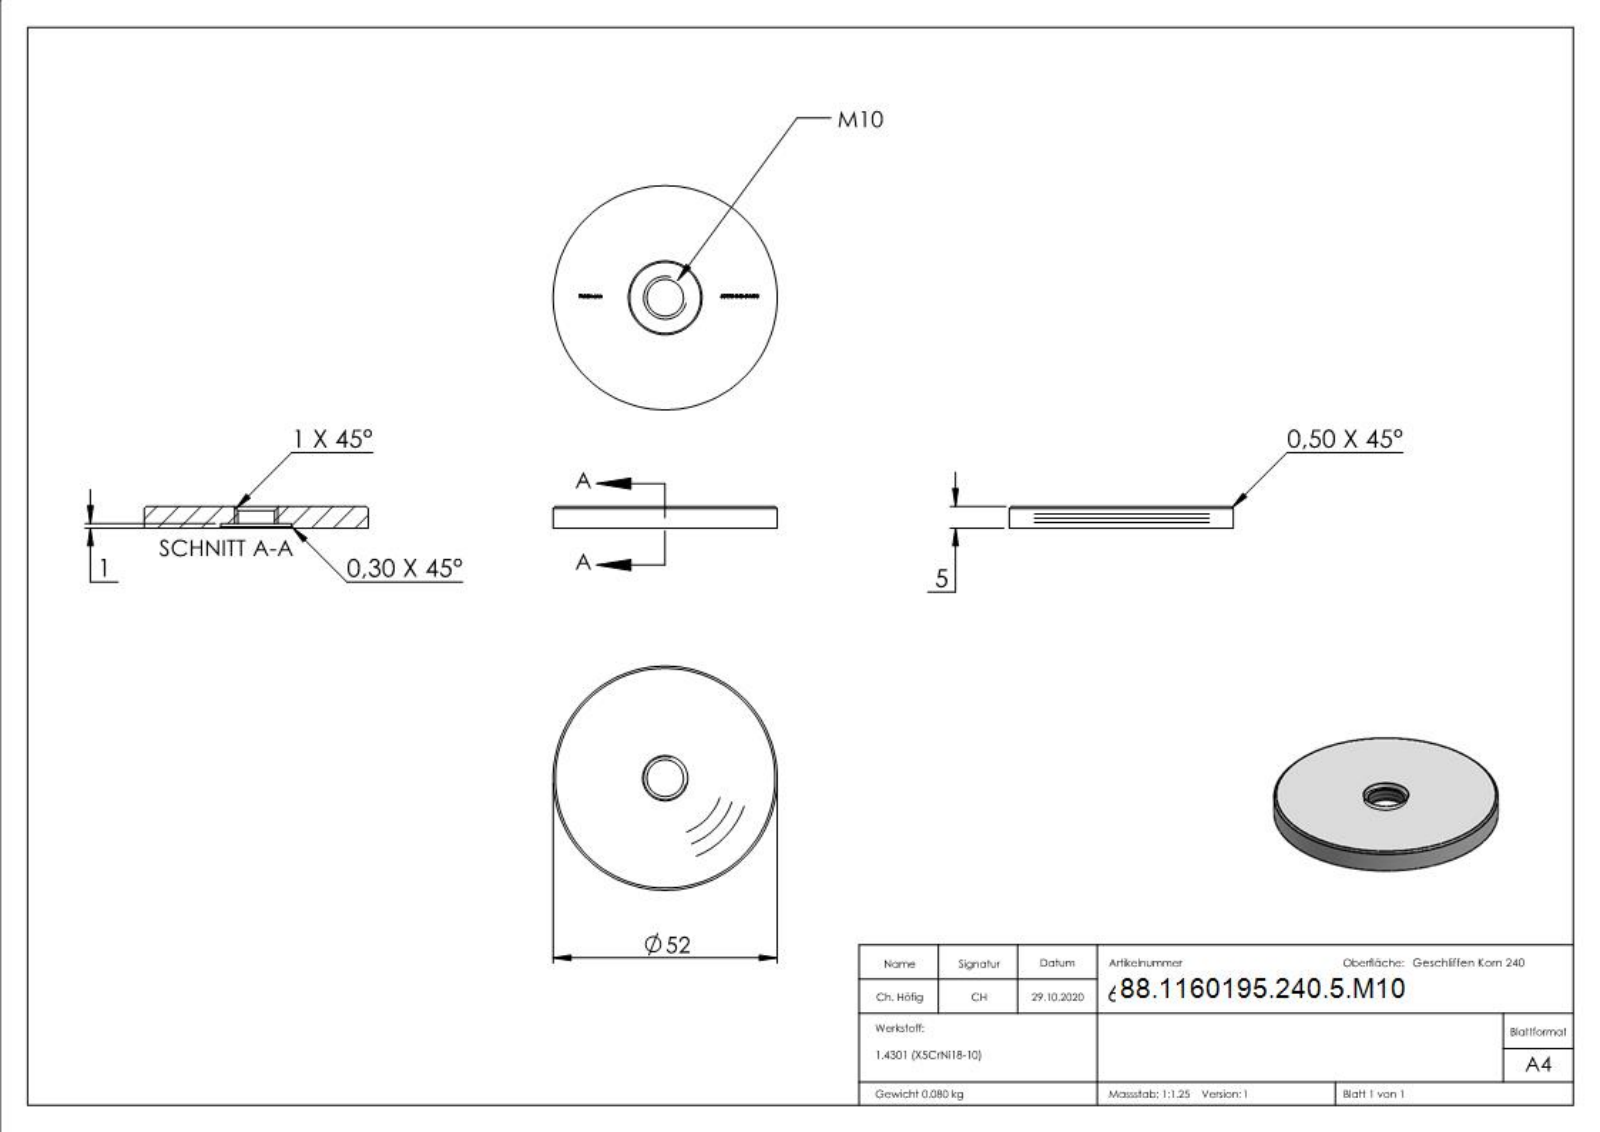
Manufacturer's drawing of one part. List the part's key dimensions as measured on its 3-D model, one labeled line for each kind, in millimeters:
Part name (STEP PRODUCT): 60195-240-5-M10
STEP written by: SolidWorks 2018 (CONFIG_CONTROL_DESIGN)
Units: millimetres
Bodies: 1 solid, 290 faces (163 planar, 6 cylindrical, 121 other)
Overall size (bounding box): 52 × 52 × 5
Volume: 10 140 mm³ · Surface area: 5 045 mm²
Round holes (diameter × count): ⌀8.5 ×1, ⌀16.5 ×1
Round bosses / shafts (diameter × count): ⌀52 ×1
Main face-to-face distances: 5, 1, 4, 0.9, 4.9, 3.44, 35.93, 0.44, 0.53, 0.75
